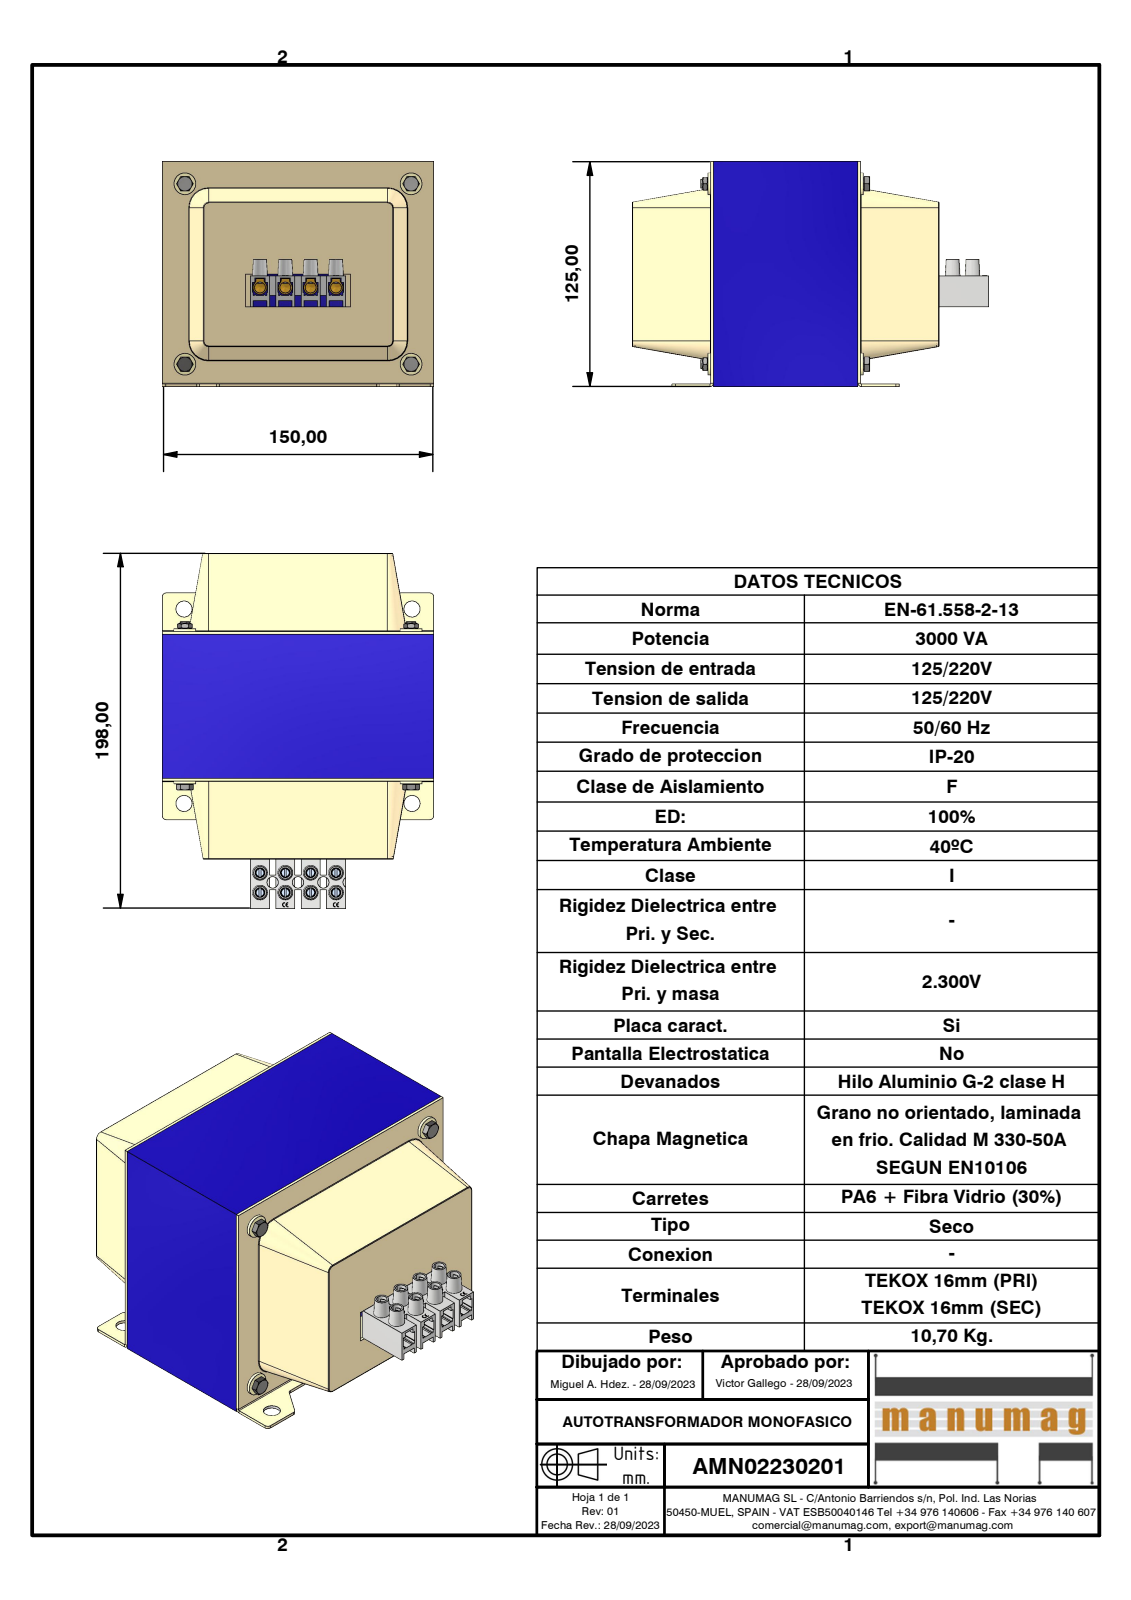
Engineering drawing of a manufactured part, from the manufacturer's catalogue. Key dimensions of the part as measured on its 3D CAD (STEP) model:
Part name (STEP PRODUCT): AMN02230201; EI150 x 125 - 80 (RC50) Azul; TAPA RC50 CIEGA; TAPA RC50 VENTANA 4 ELEMENTOS 16 (+8 more)
STEP written by: Autodesk Inventor 2023 (AUTOMOTIVE_DESIGN)
Units: millimetres
Bodies: 40 solids, 1665 faces (1108 planar, 230 cylindrical, 327 other)
Overall size (bounding box): 197.5 × 150 × 125
Volume: 1 265 000 mm³ · Surface area: 282 864 mm²
Round holes (diameter × count): ⌀3.24 ×12, ⌀5.5 ×8, ⌀6 ×8, ⌀5 ×4, ⌀8 ×4, ⌀9 ×4, ⌀6.3 ×3
Round bosses / shafts (diameter × count): ⌀4 ×8, ⌀12 ×4, ⌀6.7 ×4, ⌀5.9 ×4, ⌀4.57 ×4
Partial cylindrical surfaces — rounded edges, fillets, slot ends (radius × count): R0.38 ×16, R2.75 ×16, R2 ×14, R0.82 ×8, R3 ×8, R0.22 ×6, R0.1 ×4, R0.81 ×4
Main face-to-face distances: 125, 1.5, 25, 43.5, 100, 80, 123.5, 50, 108.12, 42
Hole centre spacings: 14, 28, 8.8, 9, 17.8, 11, 21.67, 21.75
